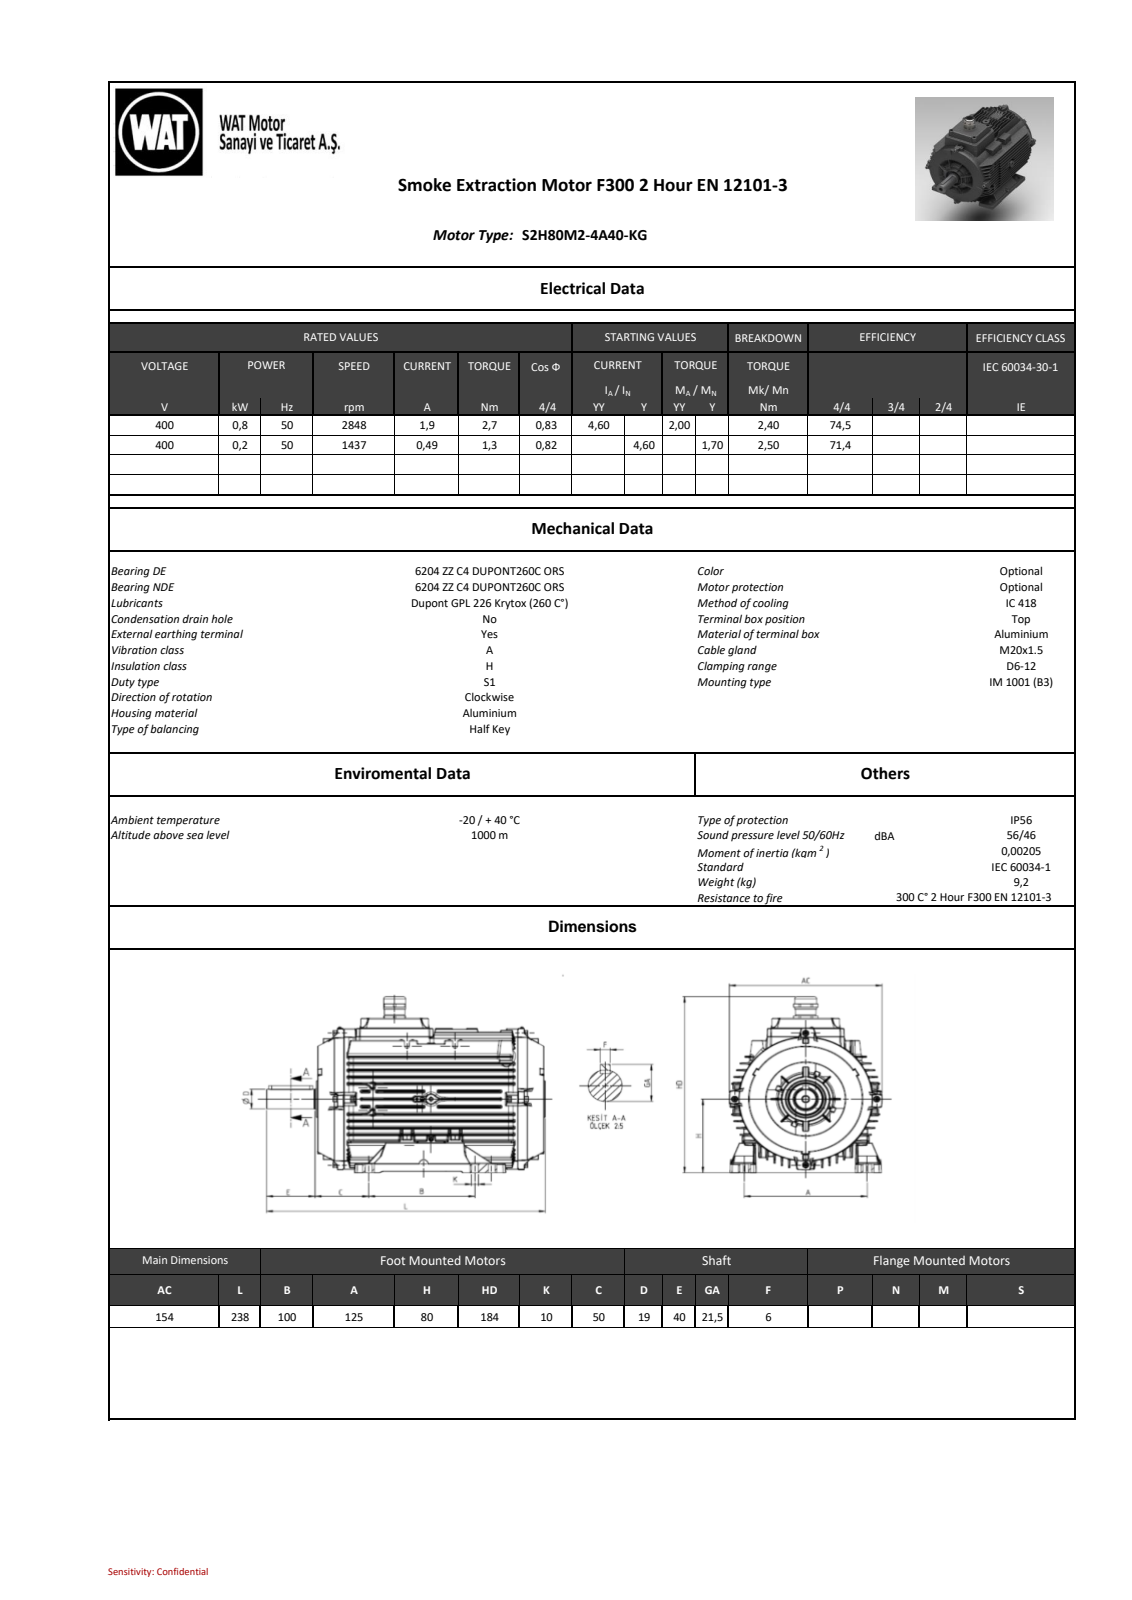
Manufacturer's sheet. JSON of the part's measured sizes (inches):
{"part_name": "2603BE5CCA1Ccwyg", "step_written_by": "SIEMENS PLM Software NX 11.0 (AUTOMOTIVE_DESIGN)", "units": "inches", "bodies": {"solids": 0, "faces": 9114, "planar": 1587, "cylindrical": 2442, "other": 5085}, "overall_size": [9.37, 8.366, 6.063], "round_holes": [[0.138, 4], [0.252, 1], [0.551, 1], [0.945, 1], [1.094, 1], [1.102, 1], [1.181, 1]], "round_bosses_or_shafts": [[0.335, 4], [0.315, 4], [0.197, 4], [0.362, 2], [5.768, 1], [1.161, 1], [0.933, 1], [0.882, 1]], "partial_cylinders_radius": [[0.02, 429], [0.039, 344], [0.031, 330], [0.008, 58], [0.079, 33], [0.197, 20], [0.157, 8], [0.315, 8]], "face_to_face_distances": [1.652, 0.408, 2.06, 0.282, 0.82, 0.413, 1.239, 2.478, 2.07, 2.342], "hole_center_spacings": [0.945, 0.945]}
